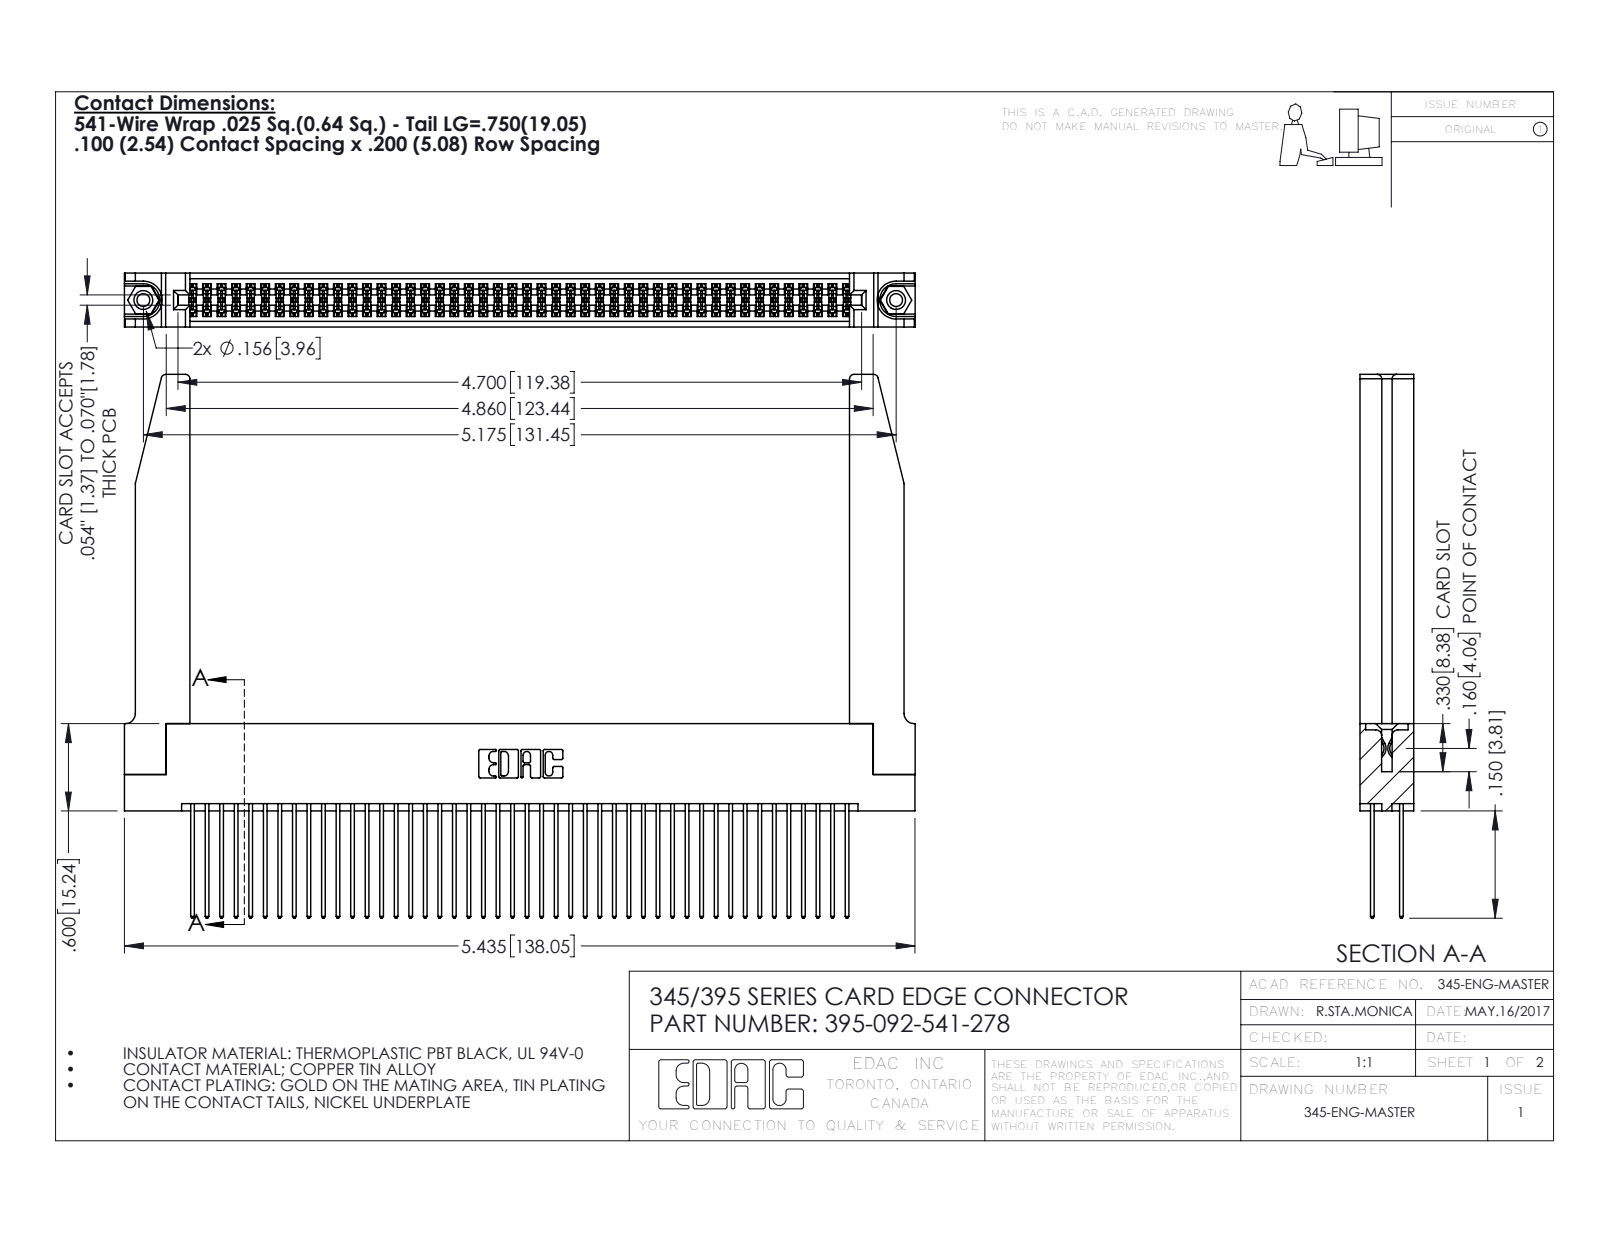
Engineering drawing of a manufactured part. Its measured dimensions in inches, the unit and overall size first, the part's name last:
Units: inches
Overall size (bounding box): 5.436 × 3.737 × 0.37
Round holes (diameter × count): ⌀0.089 ×2, ⌀0.125 ×2, ⌀0.156 ×2, ⌀0.064 ×1
Round bosses / shafts (diameter × count): ⌀0.155 ×2
Partial cylindrical surfaces — rounded edges, fillets, slot ends (radius × count): R0.006 ×138, R0.01 ×92, R0.01 ×22, R0.03 ×8, R0.007 ×6, R0.031 ×6, R0.026 ×3, R0.014 ×2
Main face-to-face distances: 0.072, 0.298, 0.37, 0.2, 0.098, 0.272, 0.025, 0.225, 0.175, 0.148
Hole centre spacings: 0.27, 4.939, 5.175
Volume: 1.327 in³ · Surface area: 46.59 in²
Bodies: 97 solids, 4960 faces (3258 planar, 1650 cylindrical, 52 other)
Part name (STEP PRODUCT): 395-092-541-278; 345-292-001_345-293-141; 345-220-078_345-220-078; 345-250-001_345-250-001-102 (+1 more)
STEP written by: SolidWorks 2016 (CONFIG_CONTROL_DESIGN)
